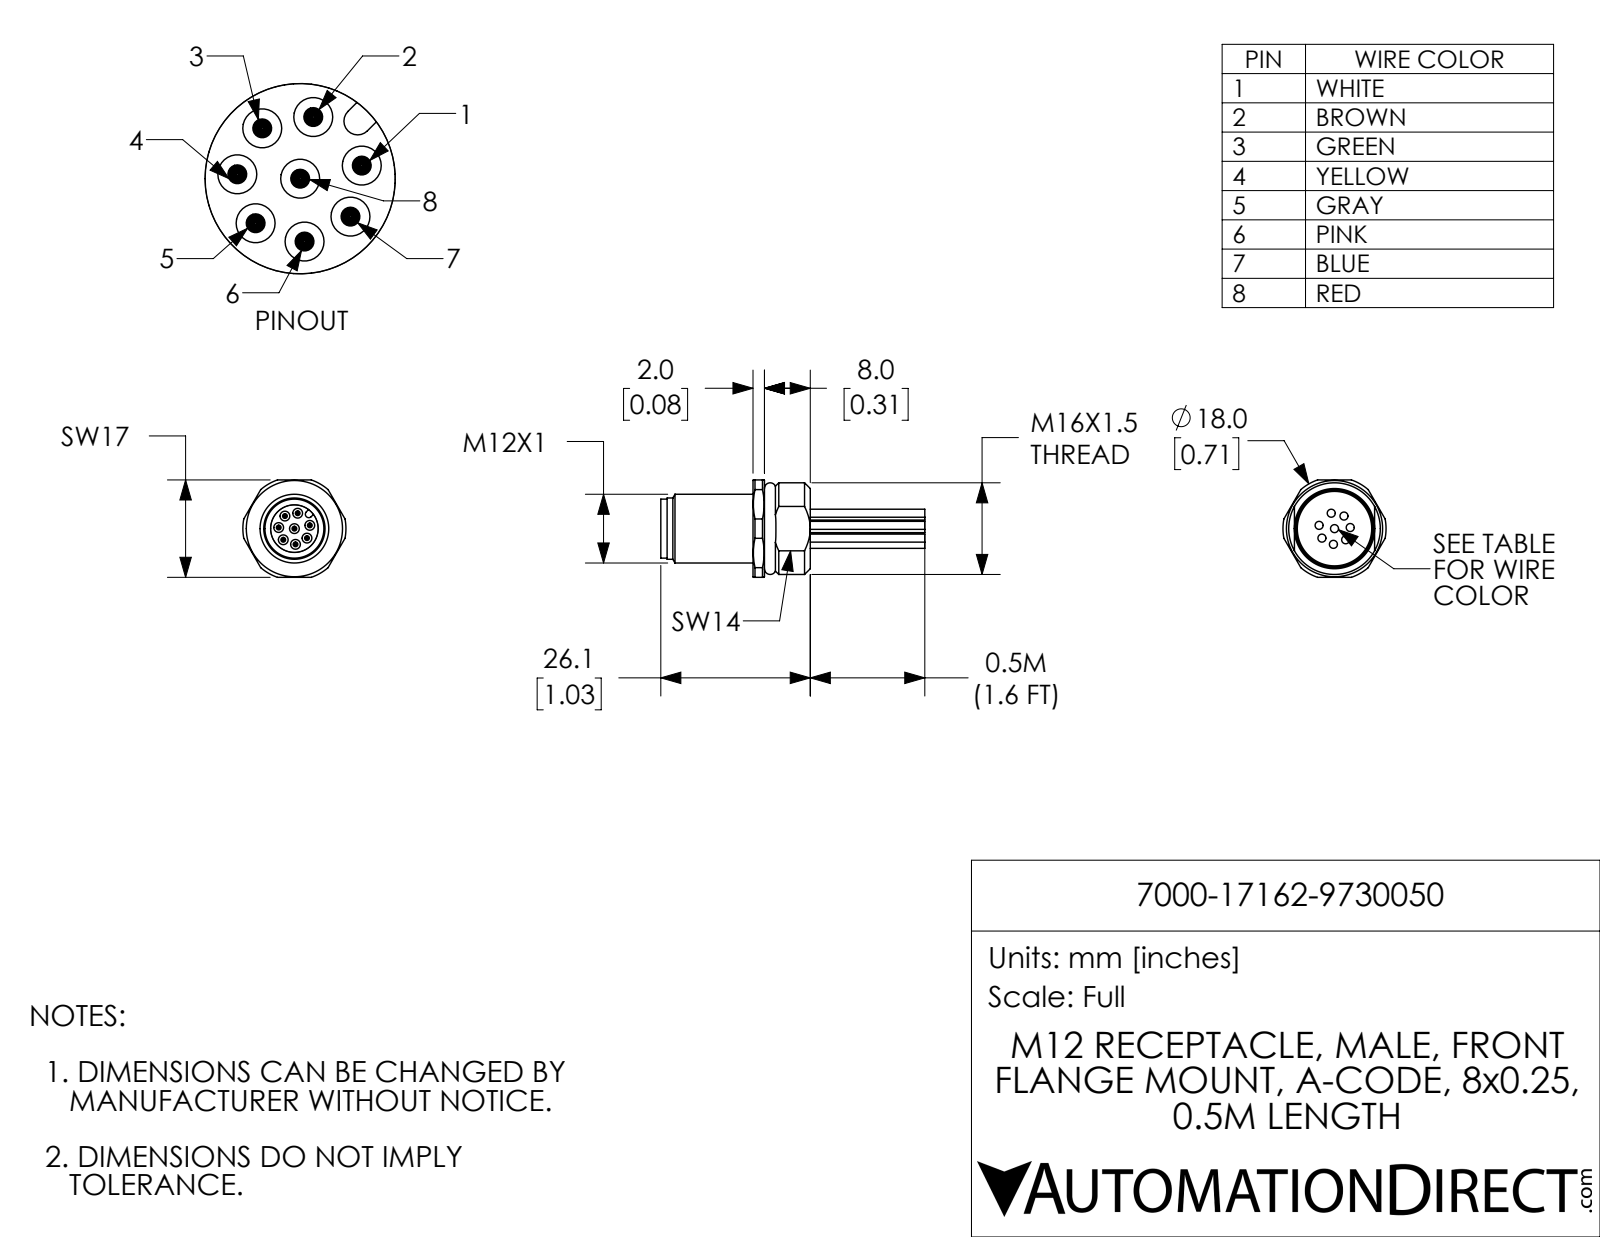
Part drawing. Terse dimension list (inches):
name: 7000-17162-9730050
written by: SolidWorks 2017 (AUTOMOTIVE_DESIGN)
unit: in
bodies: 1 solid, 142 faces (42 planar, 68 cylindrical, 32 other)
size: 1.815 × 0.709 × 0.669
volume: 0.209 in³; area: 4.364 in²
holes: 8× ⌀0.067, 1× ⌀0.327, 1× ⌀0.512
bosses: 8× ⌀0.055, 8× ⌀0.032, 1× ⌀0.472, 1× ⌀0.421, 1× ⌀0.406
rounds: 1× R0.024, 1× R0.315, 1× R0.354
face distances: 0.354, 0.276, 0.079, 0.551, 0.669, 0.638, 0.362, 0.283, 0.35, 0.988
hole spacings: 0.108, 0.163, 0.207, 0.214, 0.089, 0.09, 0.09, 0.183
